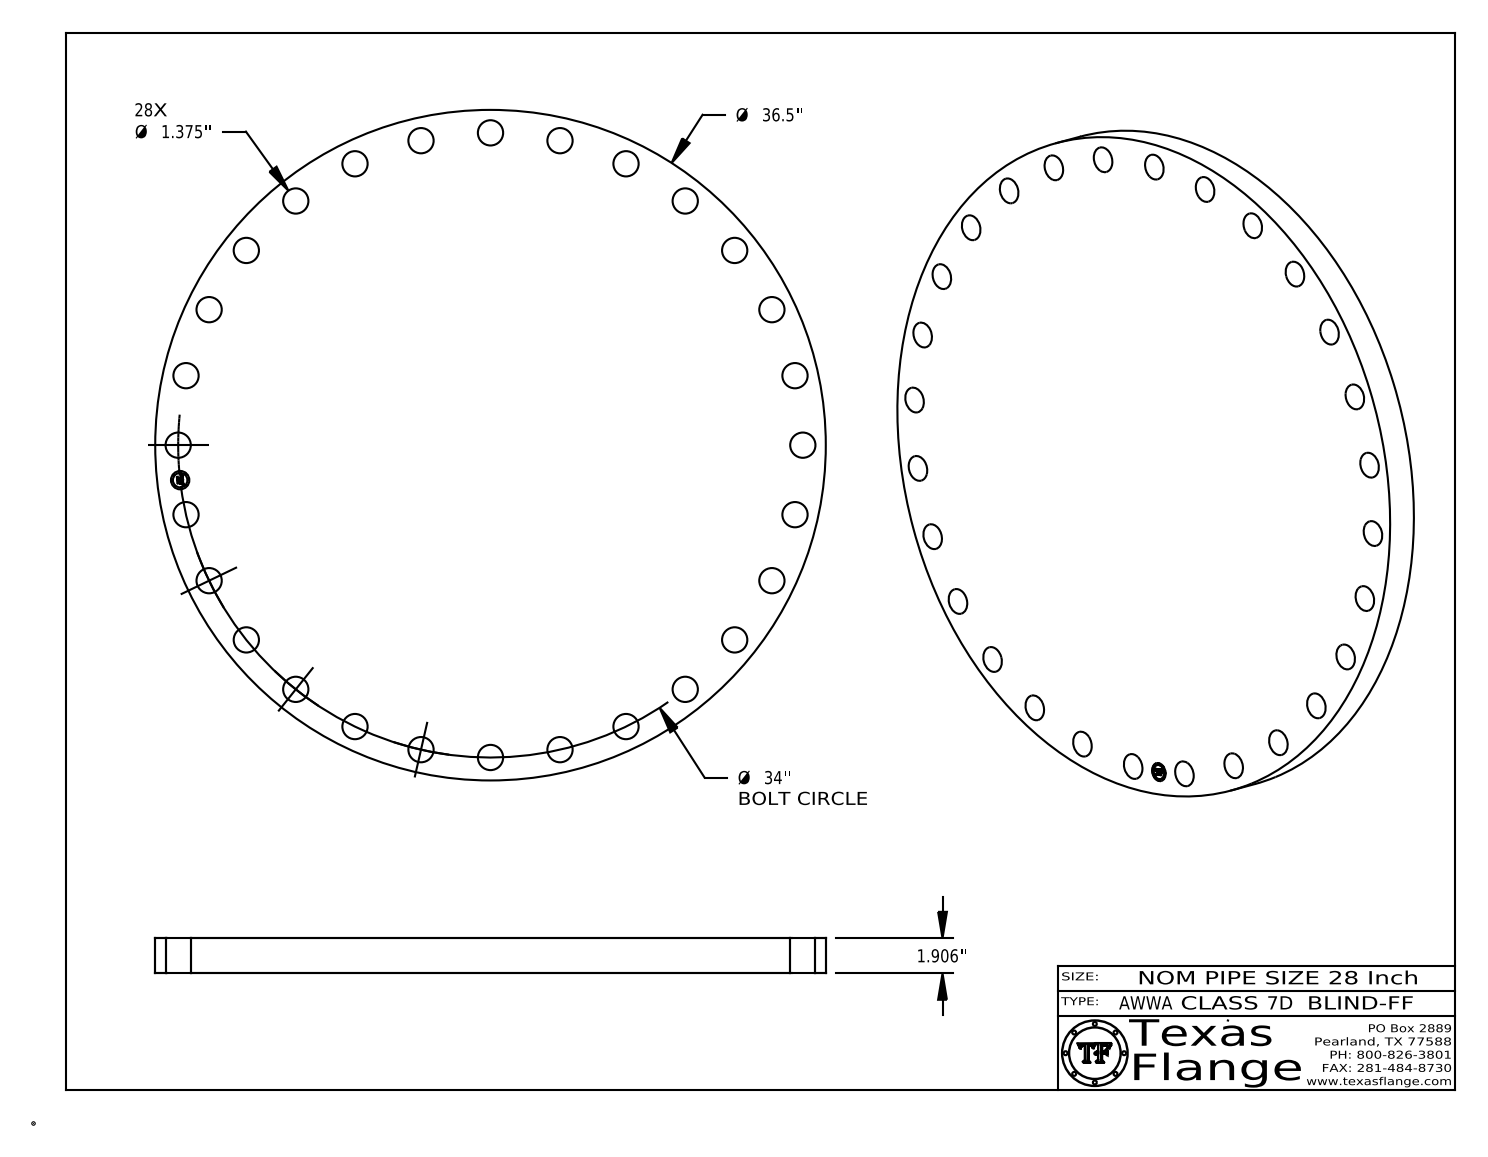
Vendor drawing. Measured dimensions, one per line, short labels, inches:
name: AWWA Class 7D-BLIND-FF
written by: CATIA V5 STEP AP214 (AUTOMOTIVE_DESIGN)
unit: in
bodies: 1 solid, 445 faces (367 planar, 78 cylindrical, 0 other)
size: 36.5 × 36.5 × 1.906
volume: 1 915 in³; area: 2 459 in²
holes: 28× ⌀1.375, 1× ⌀1
bosses: 8× ⌀0.061, 1× ⌀36.5, 1× ⌀0.788
face distances: 1.906, 0.015, 1.891, 0.298, 0.293, 0.054, 0.193, 0.248, 0.044, 0.15
hole spacings: 3.807, 7.566, 30.633, 33.786, 11.23, 18.089, 21.198, 33.147
